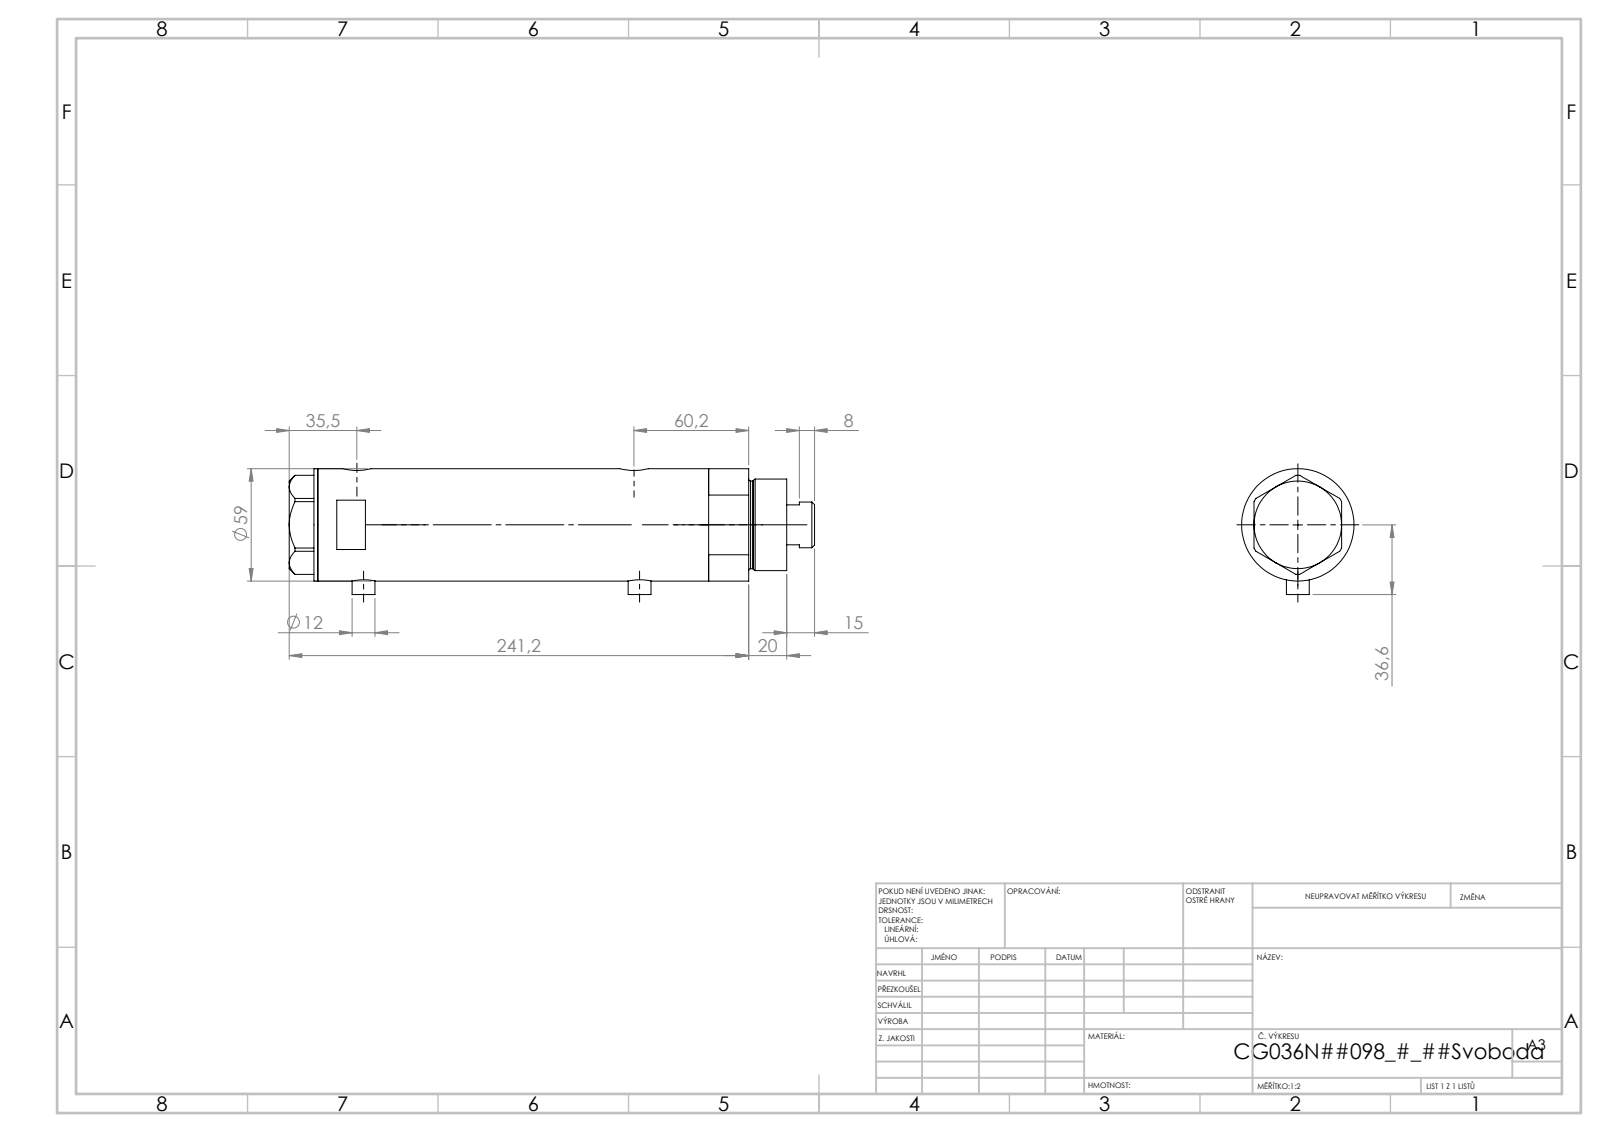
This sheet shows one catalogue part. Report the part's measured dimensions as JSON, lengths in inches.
{"part_name": "V270CG_VC; V270CG_BACK; V270CG_MIDDLE; V270CG_FRONT", "step_written_by": "SolidWorks 2019 (CONFIG_CONTROL_DESIGN)", "units": "inches", "bodies": {"solids": 4, "faces": 126, "planar": 53, "cylindrical": 53, "other": 20}, "overall_size": [10.858, 2.602, 2.323], "volume_in3": 38.45, "surface_area_in2": 194.4, "round_holes": [[0.197, 2], [0.383, 2], [0.492, 2], [0.591, 2], [0.335, 1], [0.984, 1], [1.043, 1], [1.417, 1], [1.575, 1], [2.047, 1]], "round_bosses_or_shafts": [[0.472, 2], [2.323, 1], [1.89, 1], [1.811, 1], [0.945, 1]], "face_to_face_distances": [6.583, 0.925, 5.657, 0.591, 1.516, 7.173, 0.079, 9.693, 10.283, 8.768], "hole_center_spacings": [0.114, 0.138, 5.591, 5.705, 5.728, 5.843]}
